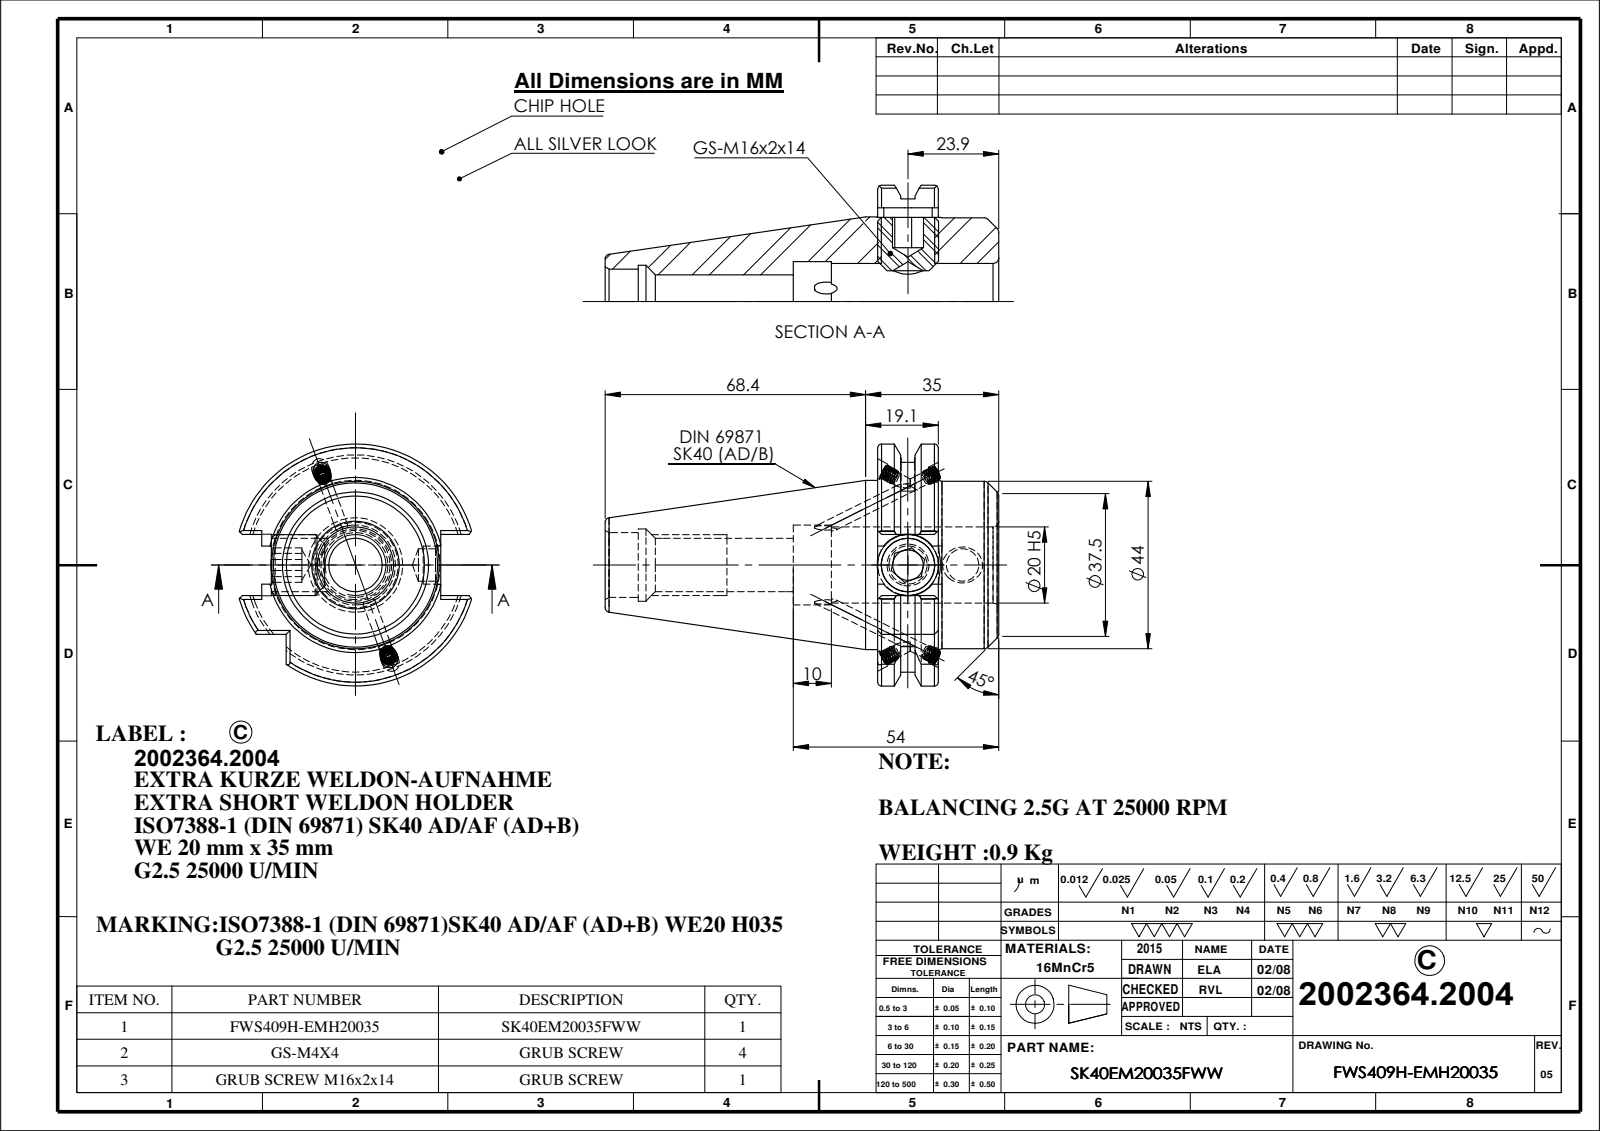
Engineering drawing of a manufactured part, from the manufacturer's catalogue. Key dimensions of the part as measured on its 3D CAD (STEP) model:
Part name (STEP PRODUCT): SK40EM20035FWW R03; GS-M4X4_DIN 913 - M4 x 4-N; GS-M16X14_ISO 4026 - M16 x 10-N; 91406-WE720035
STEP written by: SolidWorks 2018 (CONFIG_CONTROL_DESIGN)
Units: millimetres
Bodies: 6 solids, 370 faces (113 planar, 93 cylindrical, 164 other)
Overall size (bounding box): 103.4 × 63.55 × 61
Volume: 109 063 mm³ · Surface area: 27 060 mm²
Round holes (diameter × count): ⌀3.3 ×4, ⌀4.5 ×4, ⌀14 ×2, ⌀8.5 ×1, ⌀10 ×1, ⌀17 ×1, ⌀19 ×1, ⌀20 ×1, ⌀21 ×1
Round bosses / shafts (diameter × count): ⌀4 ×4, ⌀44.45 ×1, ⌀44 ×1, ⌀16 ×1
Partial cylindrical surfaces — rounded edges, fillets, slot ends (radius × count): R8.1 ×1, R28.12 ×1, R31.77 ×1
Main face-to-face distances: 15.9, 31.8, 22.2, 38.1, 54, 44.5, 16.1, 49.4, 71.6, 87.5
Hole centre spacings: 14.35
